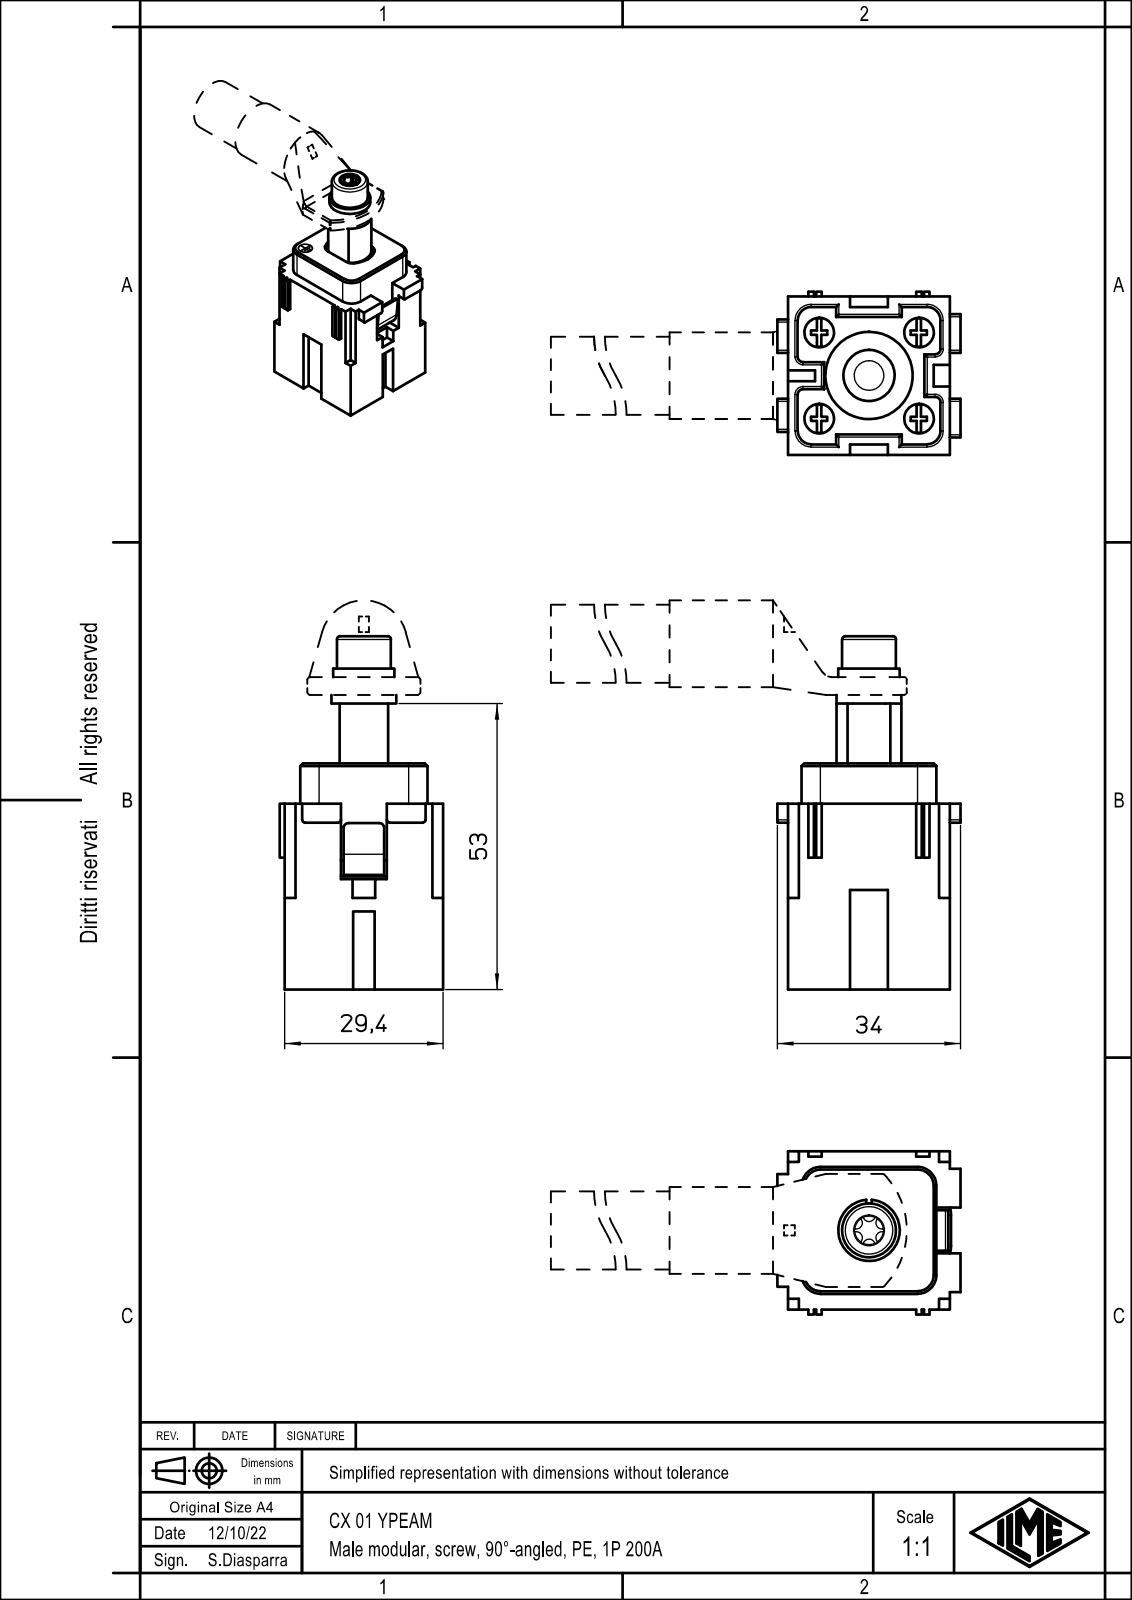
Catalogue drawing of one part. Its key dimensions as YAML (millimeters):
part_name: "CX 01 YPEAM"
step_written_by: "Creo Elements/Direct Modeling 20.1B 02-Apr-2019 (C) Parametric Technology GmbH (AUTOMOTIVE_DESIGN)"
units: millimeters
bodies: {solids: 1, faces: 367, planar: 233, cylindrical: 90, other: 44}
overall_size: [65.6, 34, 30.3]
volume: 25679
surface_area: 12316
round_holes:
  - {diameter: 4, count: 1}
  - {diameter: 16.2, count: 1}
round_bosses_or_shafts:
  - {diameter: 5.5, count: 4}
  - {diameter: 12, count: 1}
  - {diameter: 11.4, count: 1}
  - {diameter: 10, count: 1}
  - {diameter: 9.5, count: 1}
  - {diameter: 6, count: 1}
  - {diameter: 3.8, count: 1}
partial_cylinders:
  - {radius: 0.5, count: 20}
  - {radius: 1, count: 8}
  - {radius: 0.26, count: 6}
  - {radius: 1.12, count: 6}
  - {radius: 2.5, count: 4}
  - {radius: 3.5, count: 4}
  - {radius: 3.6, count: 2}
  - {radius: 4.1, count: 2}
face_to_face_distances: [30, 2, 29.4, 2.5, 1.75, 1.95, 27.45, 16, 25.5, 3.8]
hole_center_spacings: [12.38]
